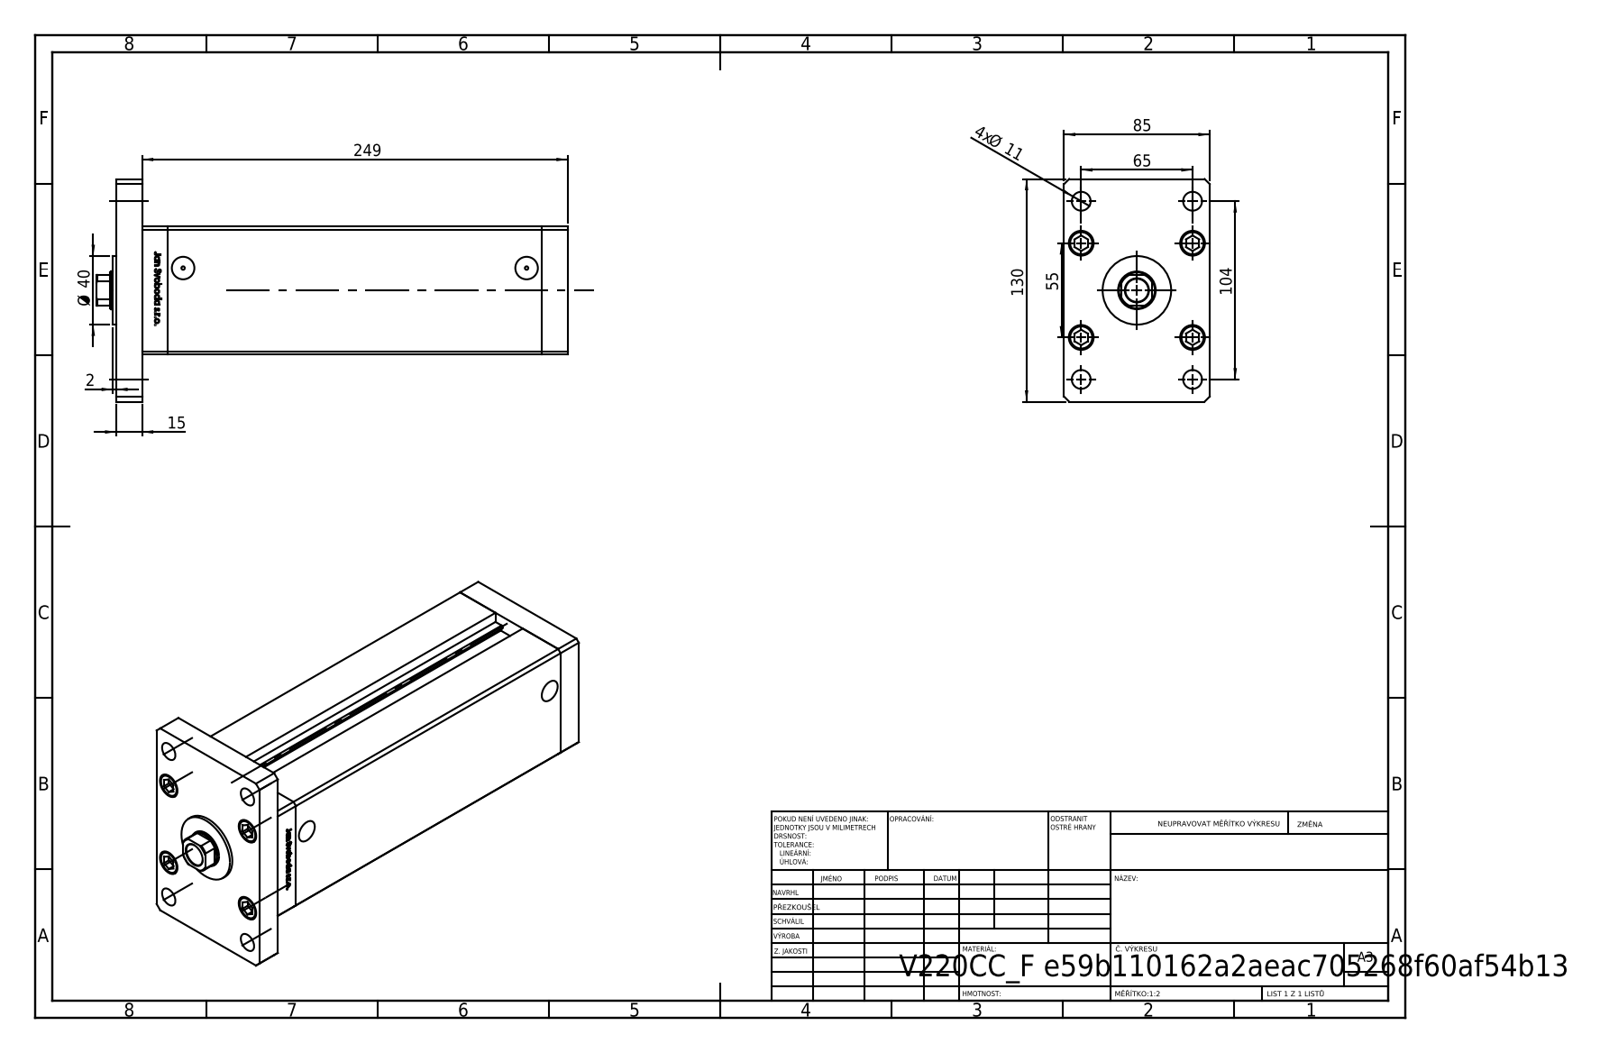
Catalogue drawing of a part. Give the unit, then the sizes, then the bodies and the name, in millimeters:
Units: millimetres
Overall size (bounding box): 275 × 130 × 85
Round holes (diameter × count): ⌀11 ×9, ⌀15.5 ×5, ⌀10 ×4, ⌀14.5 ×4, ⌀2 ×2, ⌀13.16 ×2, ⌀13.5 ×1, ⌀22 ×1, ⌀23.5 ×1
Round bosses / shafts (diameter × count): ⌀8 ×9, ⌀14.5 ×5, ⌀40 ×1
Partial cylindrical surfaces — rounded edges, fillets, slot ends (radius × count): R0.93 ×2, R10.5 ×1
Main face-to-face distances: 15, 85, 75, 233.5, 248.5, 218.5, 30, 263.5, 10.5, 27.5
Hole centre spacings: 28, 24.5, 42.57, 61.32, 65, 69.46, 79.5, 102.69
Volume: 1 536 000 mm³ · Surface area: 236 256 mm²
Bodies: 19 solids, 1308 faces (515 planar, 187 cylindrical, 606 other)
Part name (STEP PRODUCT): V220C_F_MIDDLE; V220C_VC_F; ALLEN BOLT; V220C_F (+2 more)
STEP written by: SolidWorks 2019 (CONFIG_CONTROL_DESIGN)
